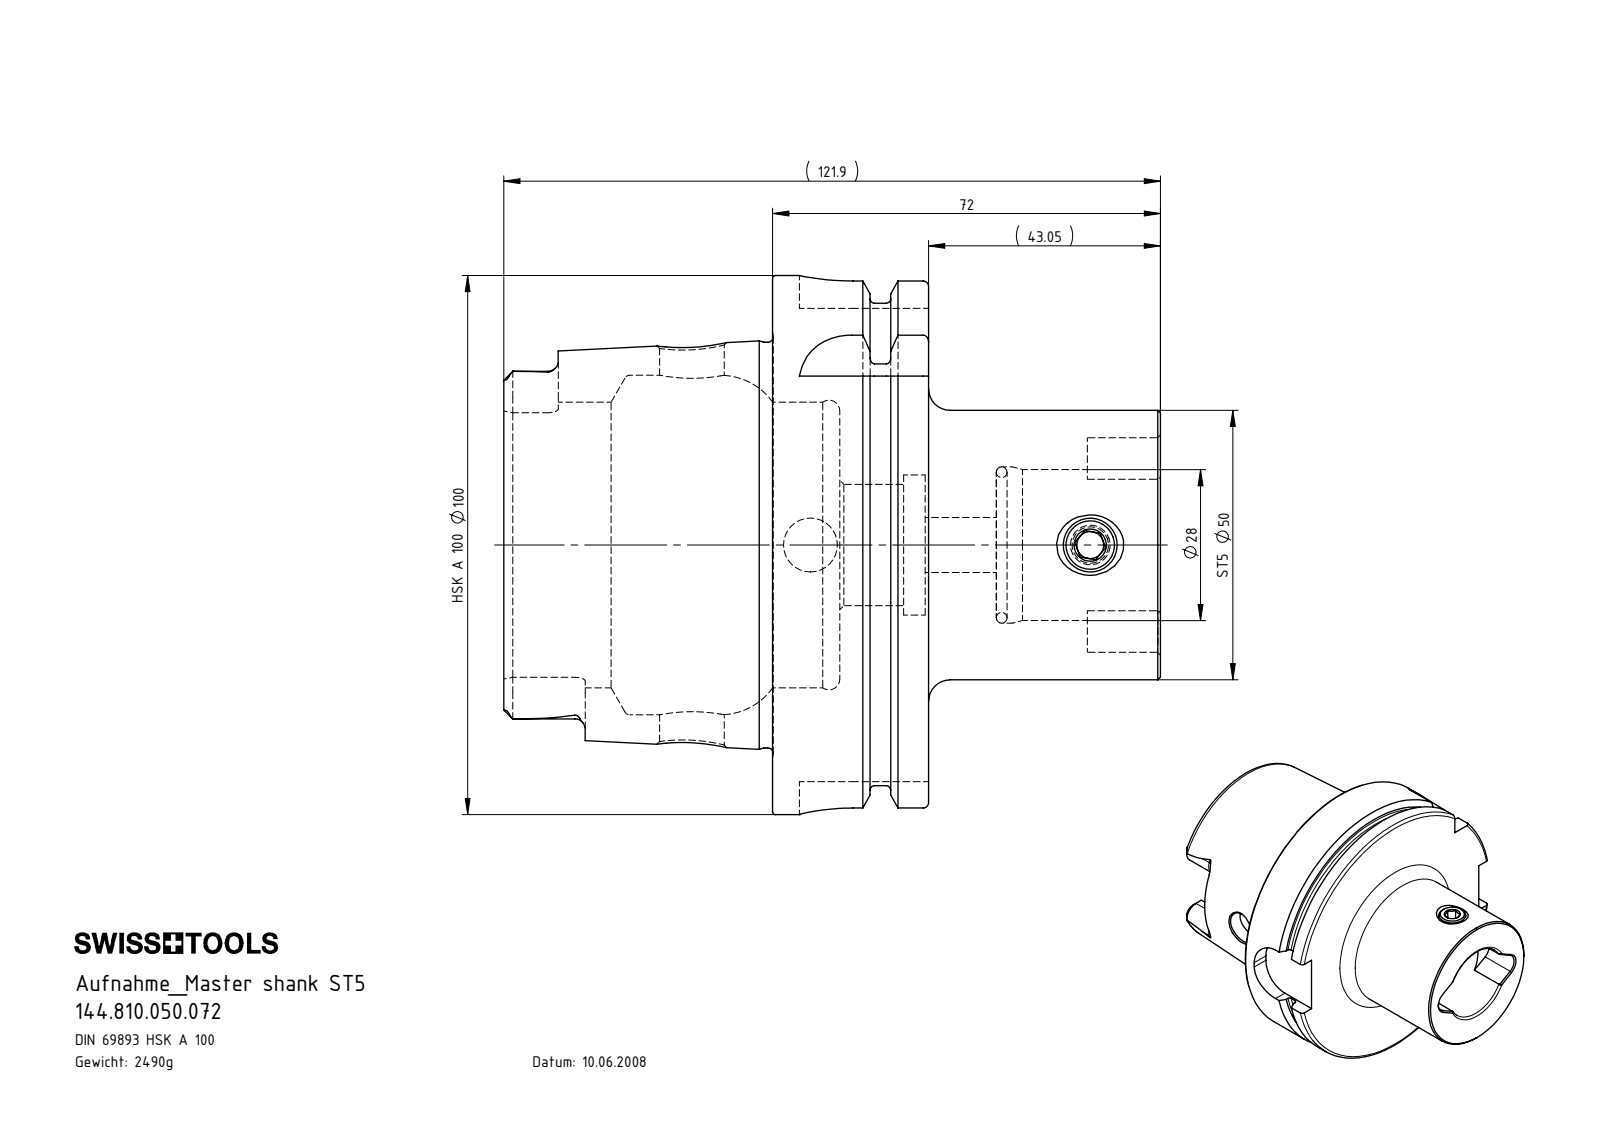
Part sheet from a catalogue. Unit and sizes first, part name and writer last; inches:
Units: inches
Overall size (bounding box): 4.799 × 3.937 × 3.937
Round holes (diameter × count): ⌀0.197 ×1, ⌀0.354 ×1, ⌀0.394 ×1, ⌀0.402 ×1, ⌀0.472 ×1, ⌀0.886 ×1, ⌀1.024 ×1, ⌀1.102 ×1, ⌀1.142 ×1, ⌀2.087 ×1, ⌀2.48 ×1
Round bosses / shafts (diameter × count): ⌀3.937 ×1, ⌀3.62 ×1, ⌀2.963 ×1, ⌀1.969 ×1, ⌀0.394 ×1
Partial cylindrical surfaces — rounded edges, fillets, slot ends (radius × count): R0.075 ×6, R0.192 ×4, R0.394 ×4, R0.165 ×2
Main face-to-face distances: 1.14, 0.49, 0.65, 2.835, 2.344, 1.695, 1.965, 2.455, 3.104, 4.799
Hole centre spacings: 2.045
Volume: 19.36 in³ · Surface area: 93.88 in²
Bodies: 3 solids, 159 faces (63 planar, 39 cylindrical, 57 other)
Part name (STEP PRODUCT): HA0.ST5.K01.072; DIN 3771 - 25x2; ST5-ER1.001.012_A; HA0-ST5.K01.072_B_Fertigbearbeitung
STEP written by: SolidWorks 2017 (AUTOMOTIVE_DESIGN)
